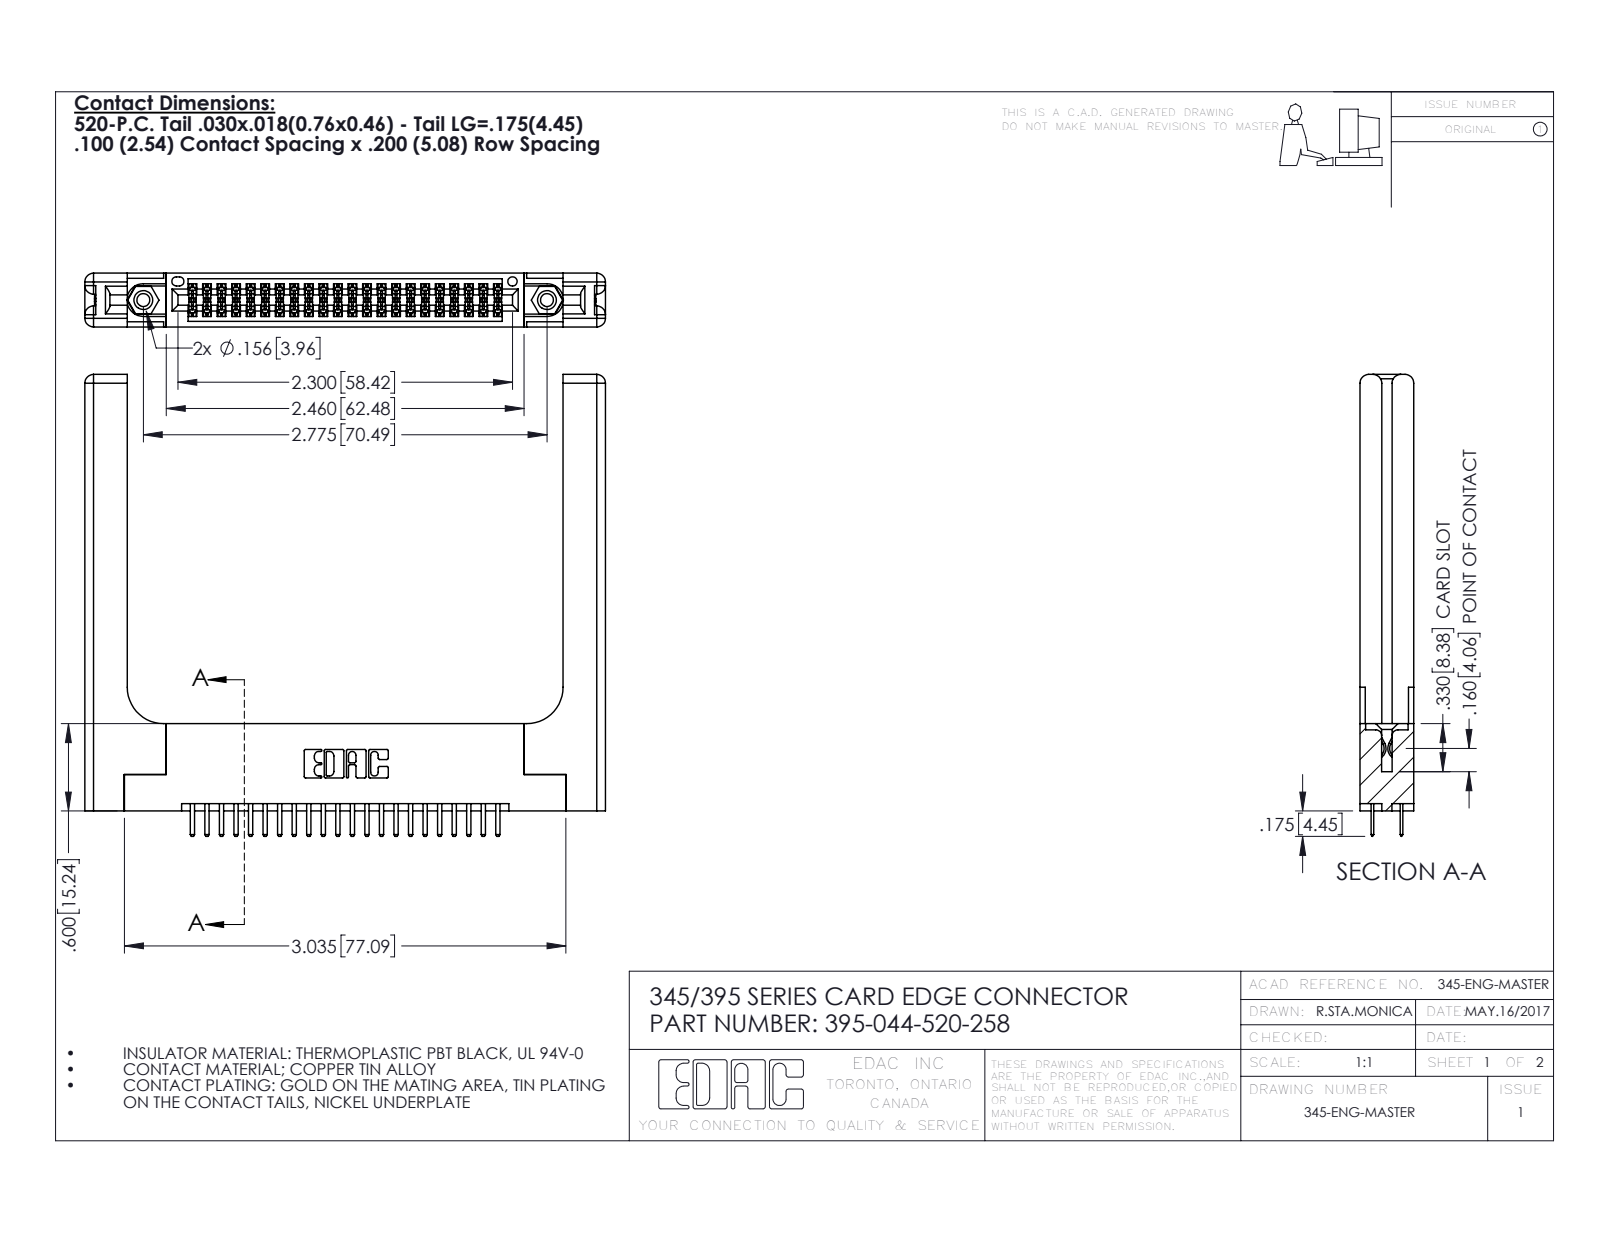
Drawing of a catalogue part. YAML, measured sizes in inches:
part_name: "395-044-520-258; 345-220-058_345-220-058; 345-292-001_345-293-120; 345 Part_Flush Mounting Lugs - 0.156 Dia-TH (+1 more)"
step_written_by: "SolidWorks 2016 (CONFIG_CONTROL_DESIGN)"
units: inches
bodies: {solids: 49, faces: 2758, planar: 1768, cylindrical: 930, other: 60}
overall_size: [3.579, 3.175, 0.37]
volume: 1.044
surface_area: 26.94
round_holes:
  - {diameter: 0.089, count: 2}
  - {diameter: 0.125, count: 2}
  - {diameter: 0.156, count: 2}
  - {diameter: 0.064, count: 1}
round_bosses_or_shafts:
  - {diameter: 0.155, count: 2}
partial_cylinders:
  - {radius: 0.006, count: 66}
  - {radius: 0.01, count: 48}
  - {radius: 0.01, count: 22}
  - {radius: 0.06, count: 16}
  - {radius: 0.007, count: 6}
  - {radius: 0.031, count: 6}
  - {radius: 0.026, count: 3}
  - {radius: 0.014, count: 2}
face_to_face_distances: [0.37, 0.072, 0.298, 0.2, 0.15, 0.148, 0.077, 0.22, 0.098, 0.272]
hole_center_spacings: [0.27, 2.541, 2.775]
